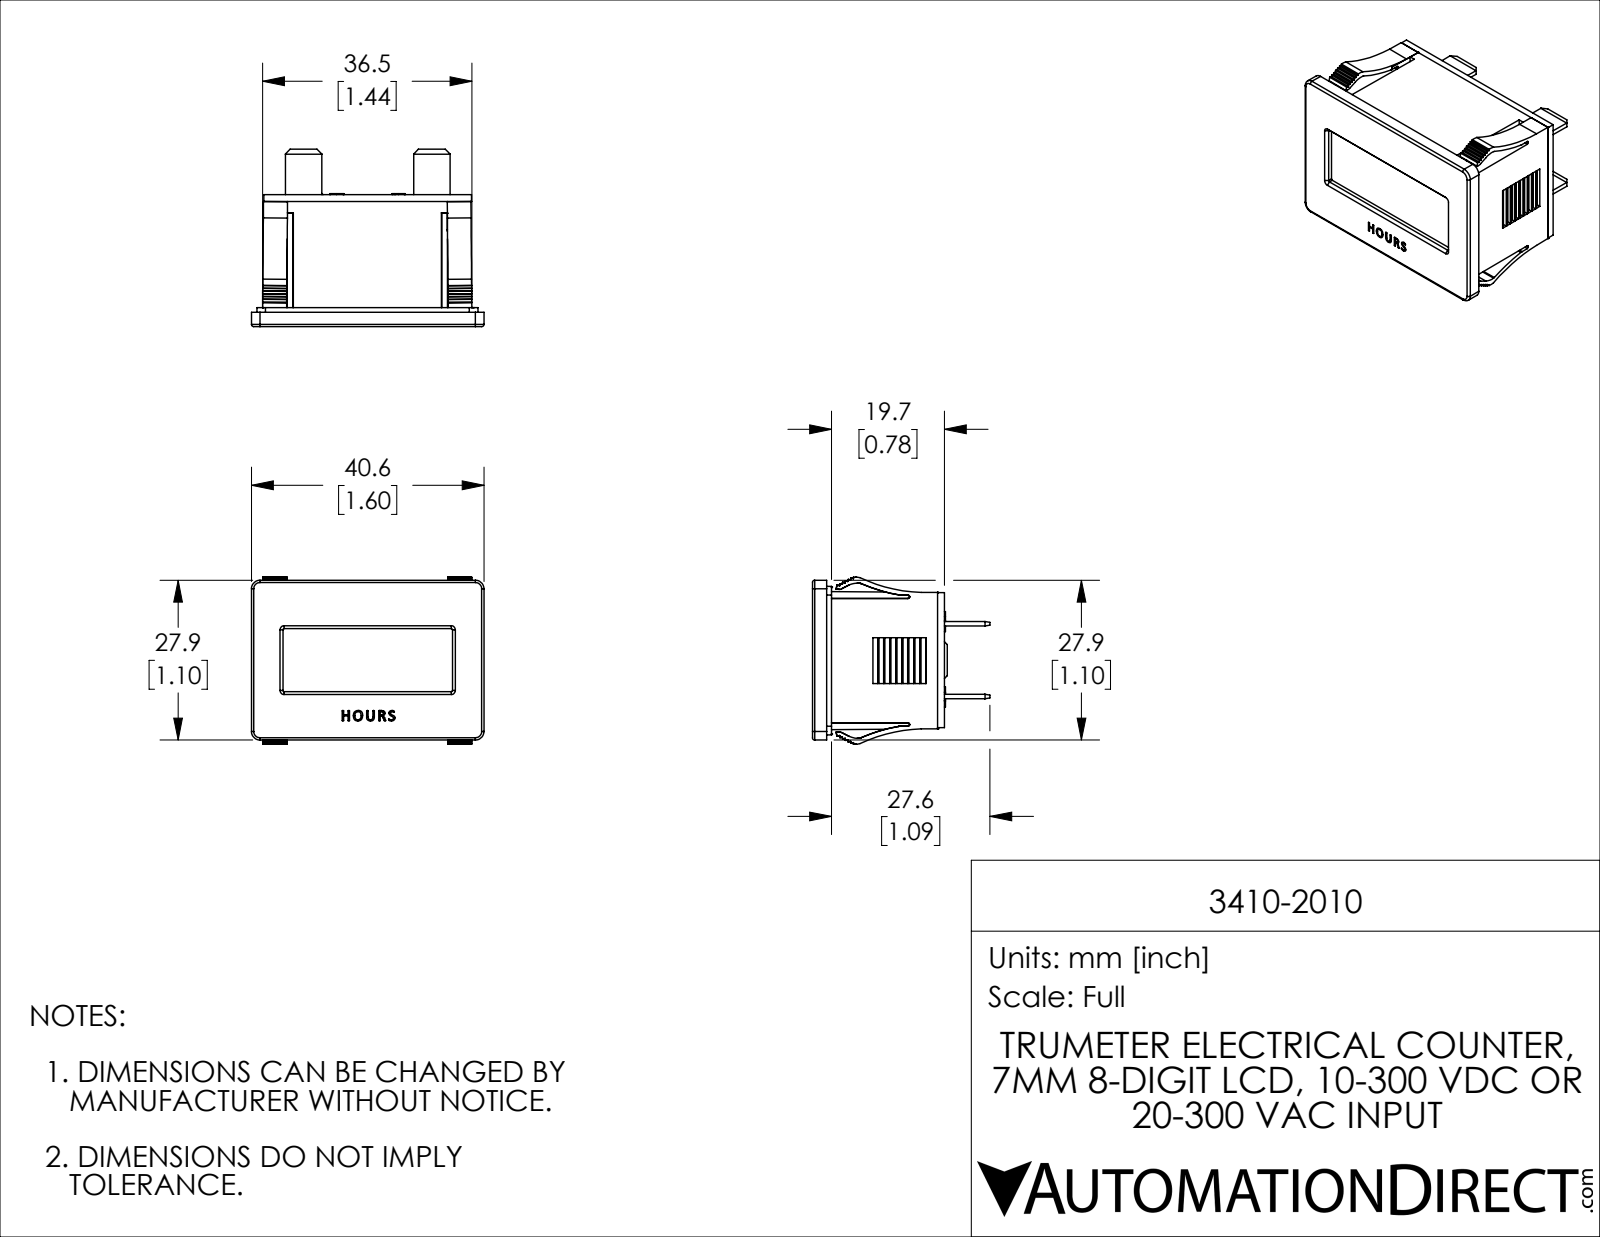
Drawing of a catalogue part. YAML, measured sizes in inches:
part_name: "3410-2010"
step_written_by: "SolidWorks 2021 (CONFIG_CONTROL_DESIGN)"
units: inches
bodies: {solids: 1, faces: 722, planar: 496, cylindrical: 78, other: 148}
overall_size: [1.598, 1.22, 1.148]
volume: 1.234
surface_area: 12.16
partial_cylinders:
  - {radius: 0.059, count: 8}
  - {radius: 0.01, count: 6}
  - {radius: 0.008, count: 4}
  - {radius: 0.016, count: 4}
  - {radius: 0.03, count: 4}
  - {radius: 0.006, count: 2}
  - {radius: 0.01, count: 2}
  - {radius: 0.015, count: 2}
face_to_face_distances: [0.047, 0.86, 0.907, 0.048, 0.859, 0.031, 0.811, 0.813, 0.5, 0.828]
